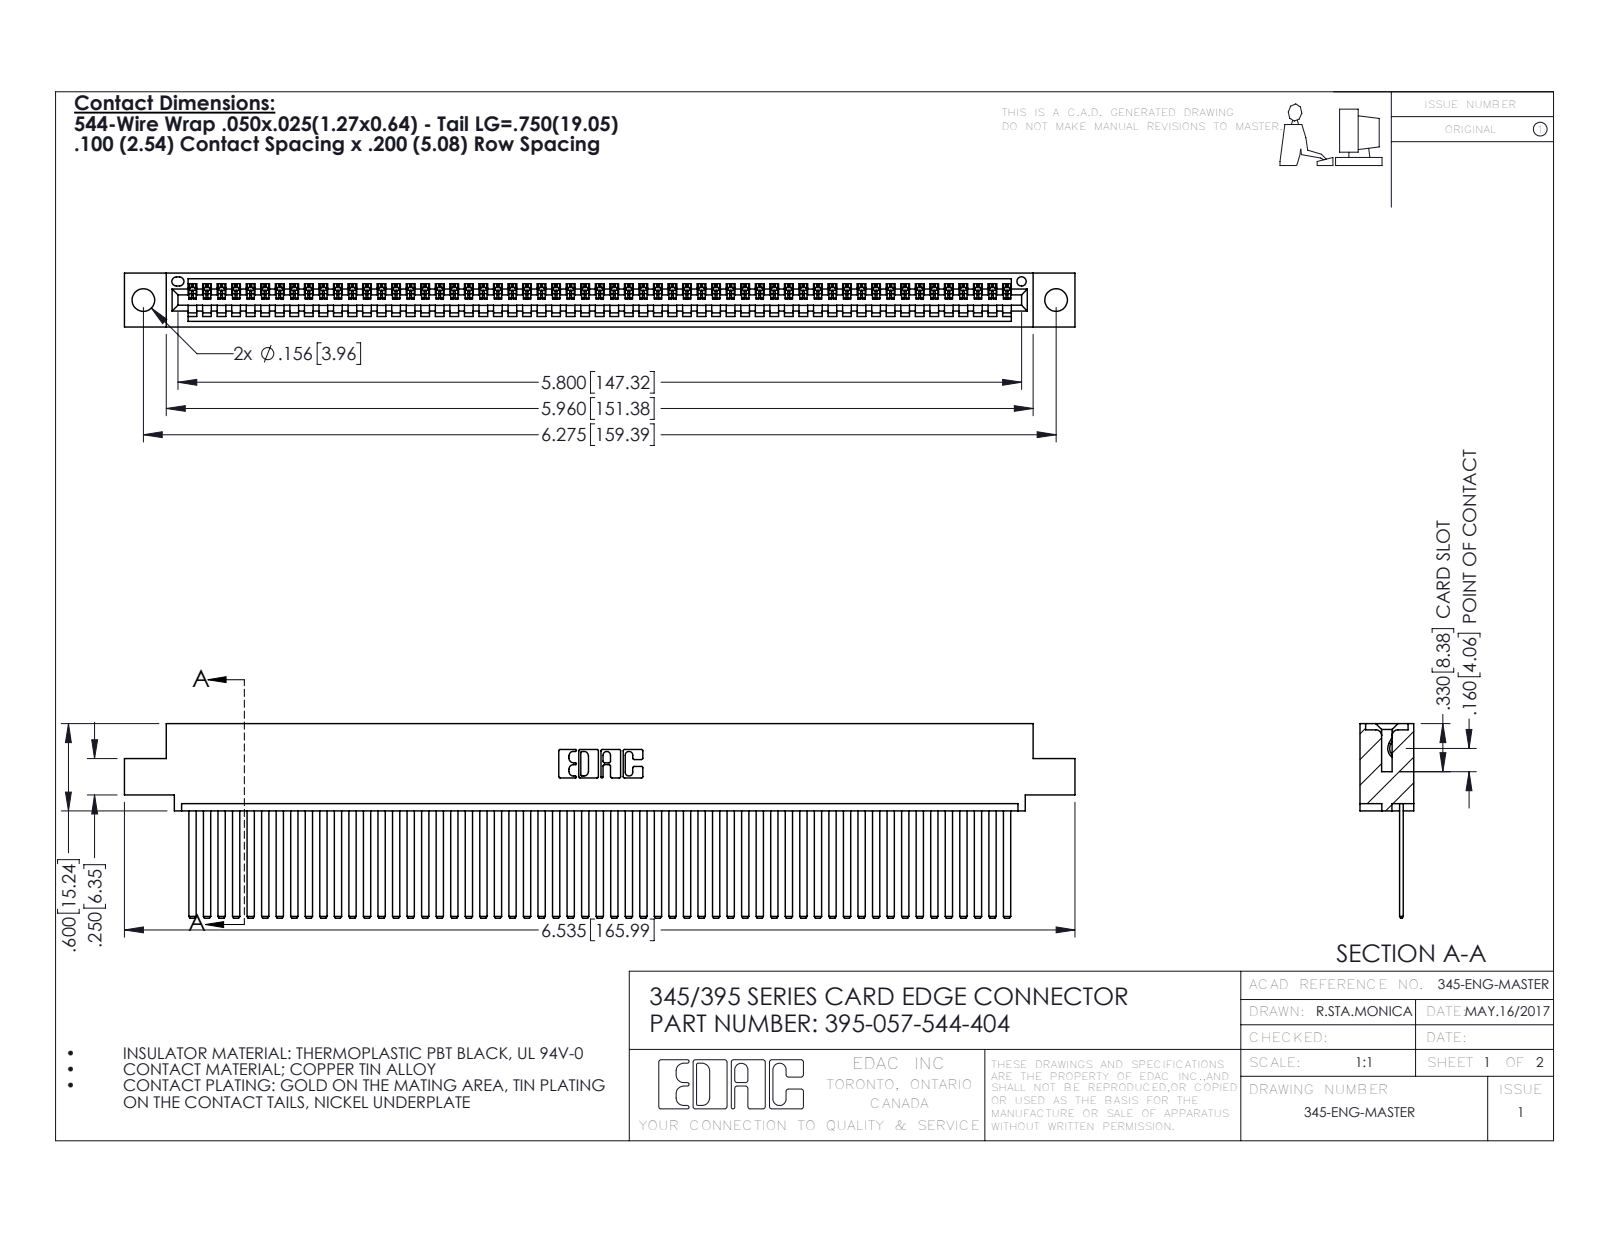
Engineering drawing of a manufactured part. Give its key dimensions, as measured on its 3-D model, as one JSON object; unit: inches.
{"part_name": "345 Part_0.110 Offset - 0.156 Dia-TH; 395-057-544-404; 345-292-001_345-293-144", "step_written_by": "SolidWorks 2016 (CONFIG_CONTROL_DESIGN)", "units": "inches", "bodies": {"solids": 58, "faces": 3094, "planar": 2136, "cylindrical": 958, "other": 0}, "overall_size": [6.535, 1.337, 0.37], "volume_in3": 1, "surface_area_in2": 36.97, "round_holes": [[0.156, 2], [0.064, 1]], "partial_cylinders_radius": [[0.006, 114], [0.01, 22], [0.007, 6], [0.031, 6], [0.026, 3], [0.031, 2], [0.04, 2], [0.014, 1]], "face_to_face_distances": [0.072, 0.298, 0.025, 0.098, 0.272, 0.37, 0.2, 0.225, 0.149, 0.072], "hole_center_spacings": [0.27, 6.039, 6.275]}
